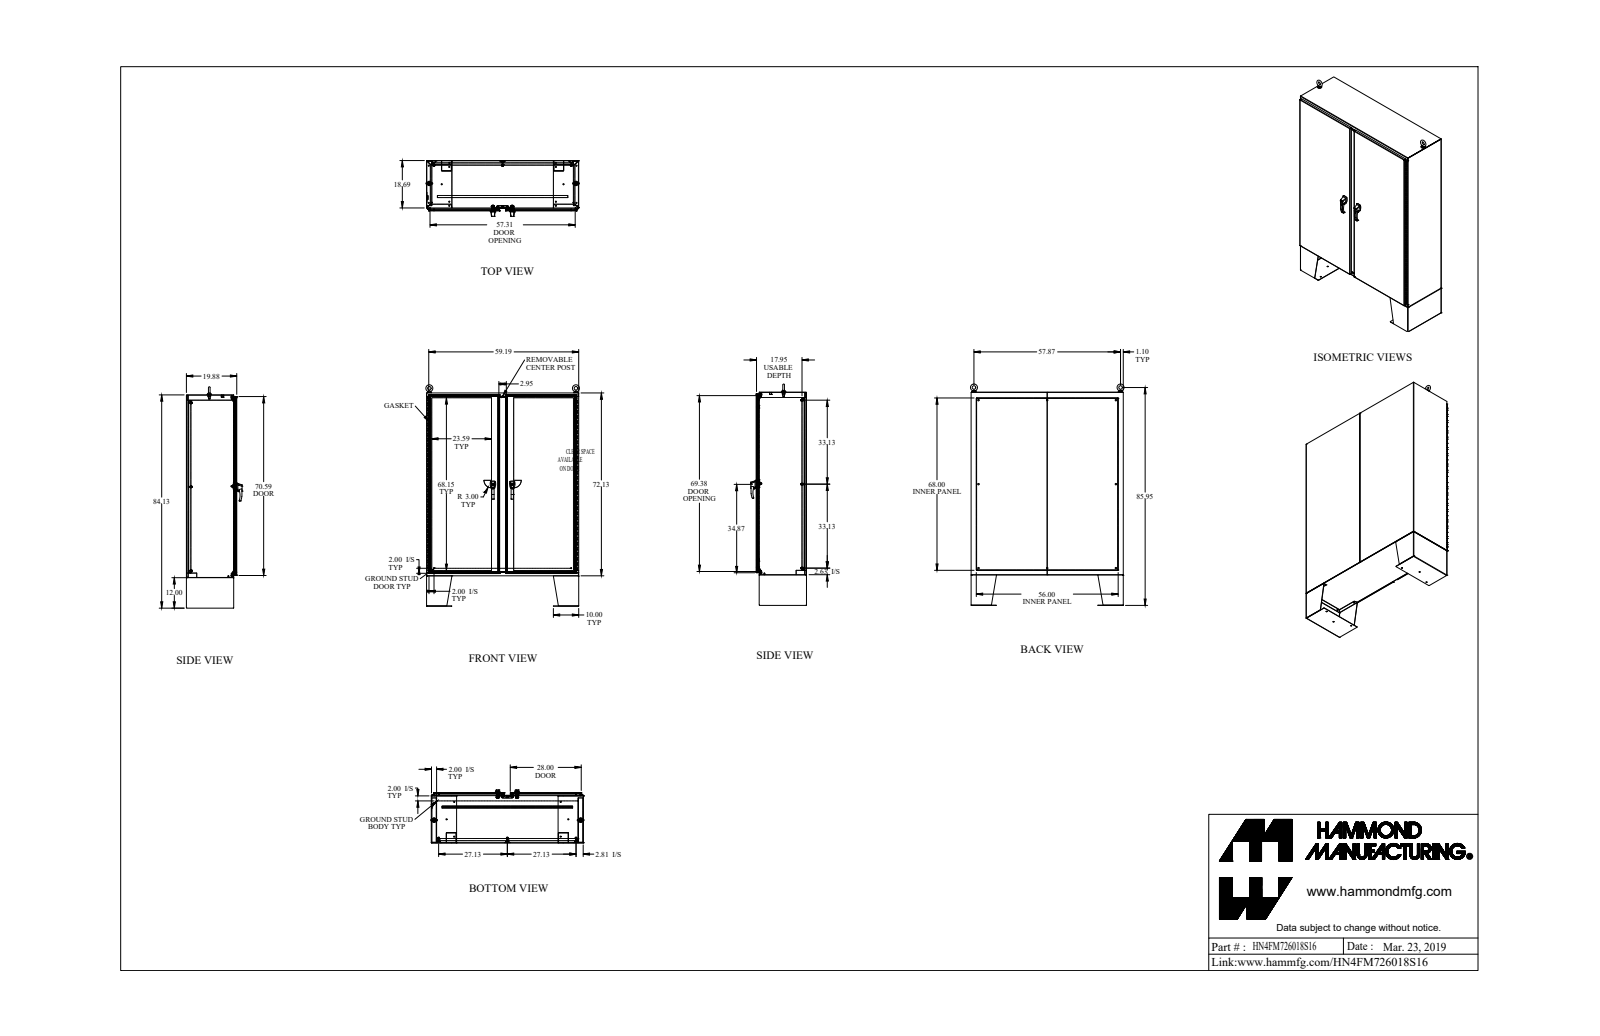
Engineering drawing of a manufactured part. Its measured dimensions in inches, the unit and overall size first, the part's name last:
Units: inches
Overall size (bounding box): 87.321 × 60.607 × 21.99
Round holes (diameter × count): ⌀0.304 ×24, ⌀0.437 ×14, ⌀0.307 ×8, ⌀0.35 ×8, ⌀0.563 ×8, ⌀0.445 ×7, ⌀0.25 ×6, ⌀0.281 ×4, ⌀0.313 ×4, ⌀0.39 ×4, ⌀0.201 ×3, ⌀0.313 ×3
Round bosses / shafts (diameter × count): ⌀1 ×10, ⌀0.65 ×8, ⌀0.375 ×8, ⌀0.332 ×8, ⌀0.75 ×4, ⌀0.625 ×4, ⌀0.44 ×4, ⌀0.37 ×4
Partial cylindrical surfaces — rounded edges, fillets, slot ends (radius × count): R0.5 ×33, R0.018 ×32, R0.125 ×32, R0.048 ×29, R0.143 ×29, R0.06 ×28, R0.03 ×12, R0.09 ×12
Main face-to-face distances: 0.095, 0.095, 19.78, 19.685, 0.125, 19.875, 19.78, 17.998, 1.782, 1.687
Hole centre spacings: 6, 12, 18, 24, 30, 36, 42, 7.487
Volume: 2 224 in³ · Surface area: 44 924 in²
Bodies: 135 solids, 4022 faces (1842 planar, 1819 cylindrical, 361 other)
Part name (STEP PRODUCT): HN4FM726018S16
STEP written by: SolidWorks 2018 (AUTOMOTIVE_DESIGN)
